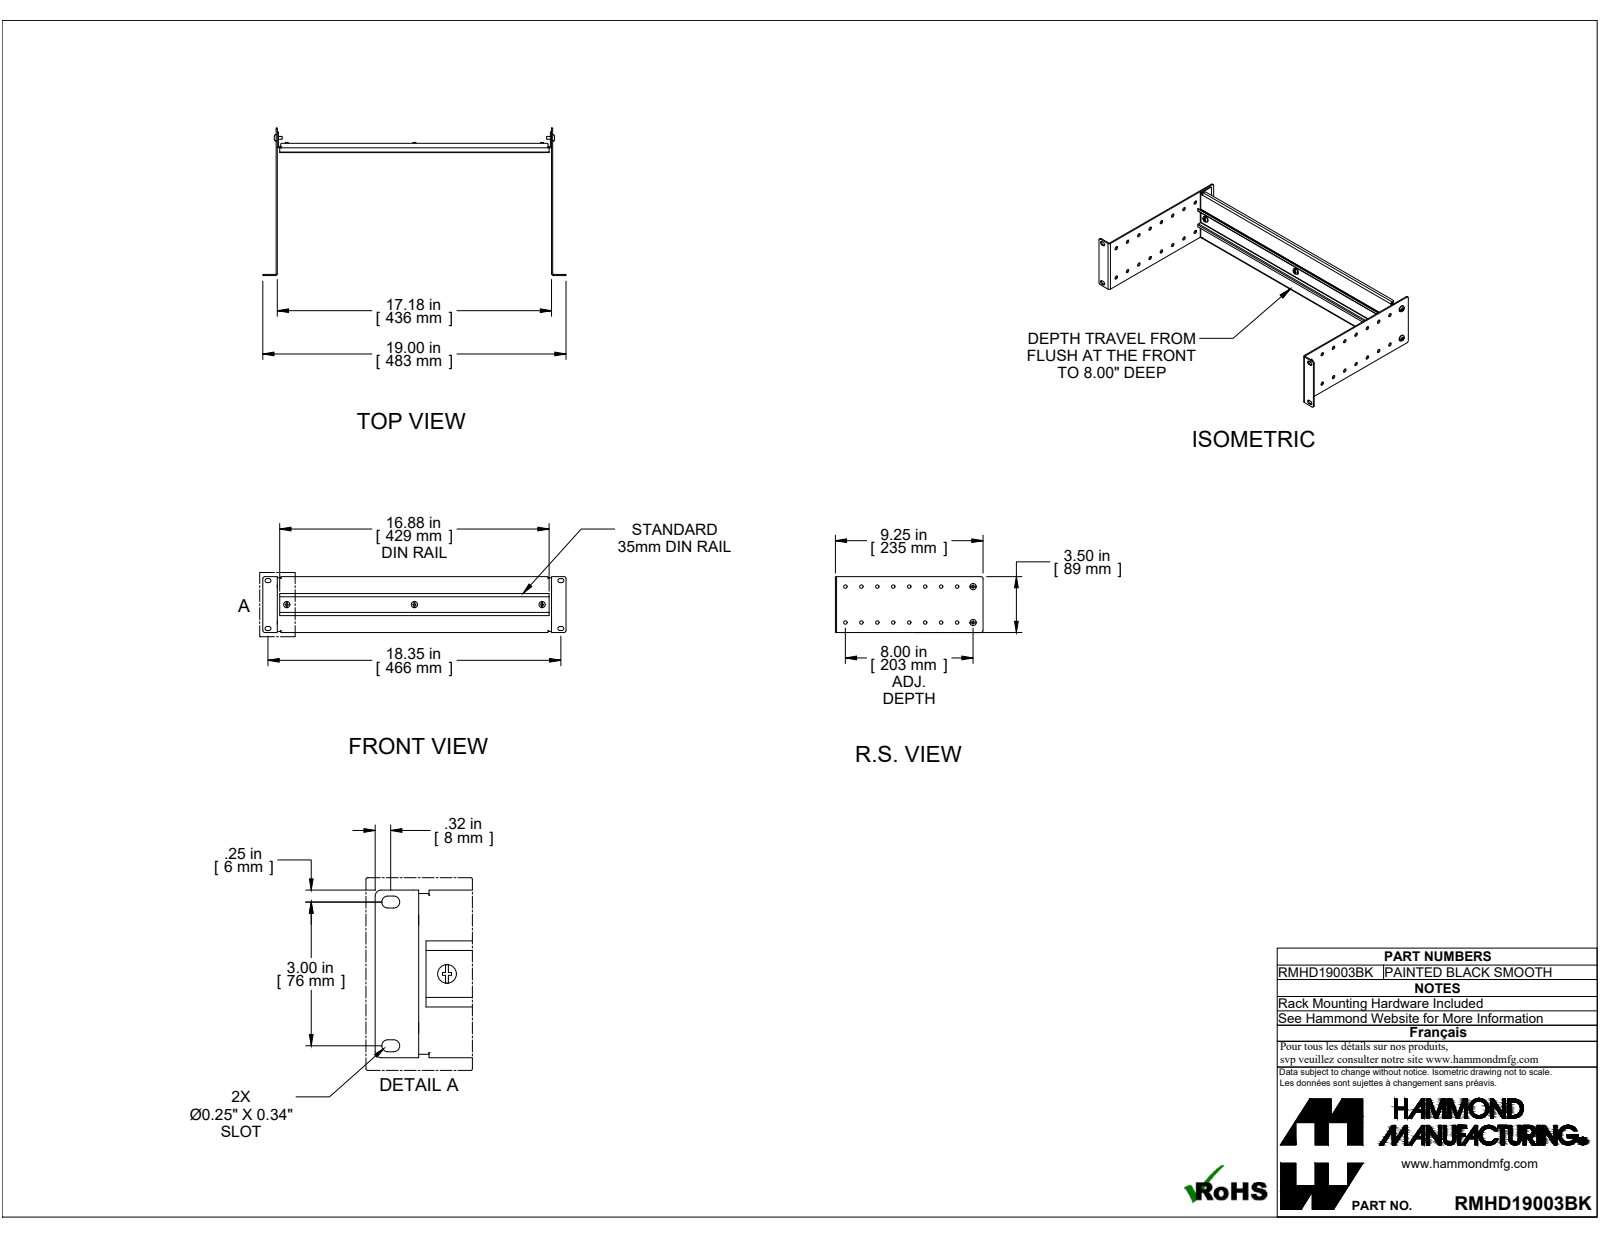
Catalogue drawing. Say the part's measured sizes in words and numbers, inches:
The part is named "RMHD19003BK". Its 3-D file was written by "SolidWorks 2019 (AUTOMOTIVE_DESIGN)". It is 11 solids with 298 faces: 181 planar, 96 cylindrical and 21 other. Overall it measures 19 by 9.25 by 3.5 inches. Its volume is 11.38 cubic inches and its surface area 358.4 square inches. Round holes: 39 of diameter 0.218, 5 of diameter 0.177. Round bosses or shafts: 7 of diameter 0.39, 7 of diameter 0.18. Partial cylindrical surfaces (rounded edges, fillets, slot ends): 15 of radius 0.125, 6 of radius 0.036, 6 of radius 0.108, 4 of radius 0.018, 4 of radius 0.054. The main face-to-face distances are 0.072, 0.072, 17.252, 17.18, 17.324, 0.036, 0.108, 8, 0.264, 1.224. The hole center spacings are 2.462, 3.01, 1, 3.75, 2, 4.589, 3, 4.
